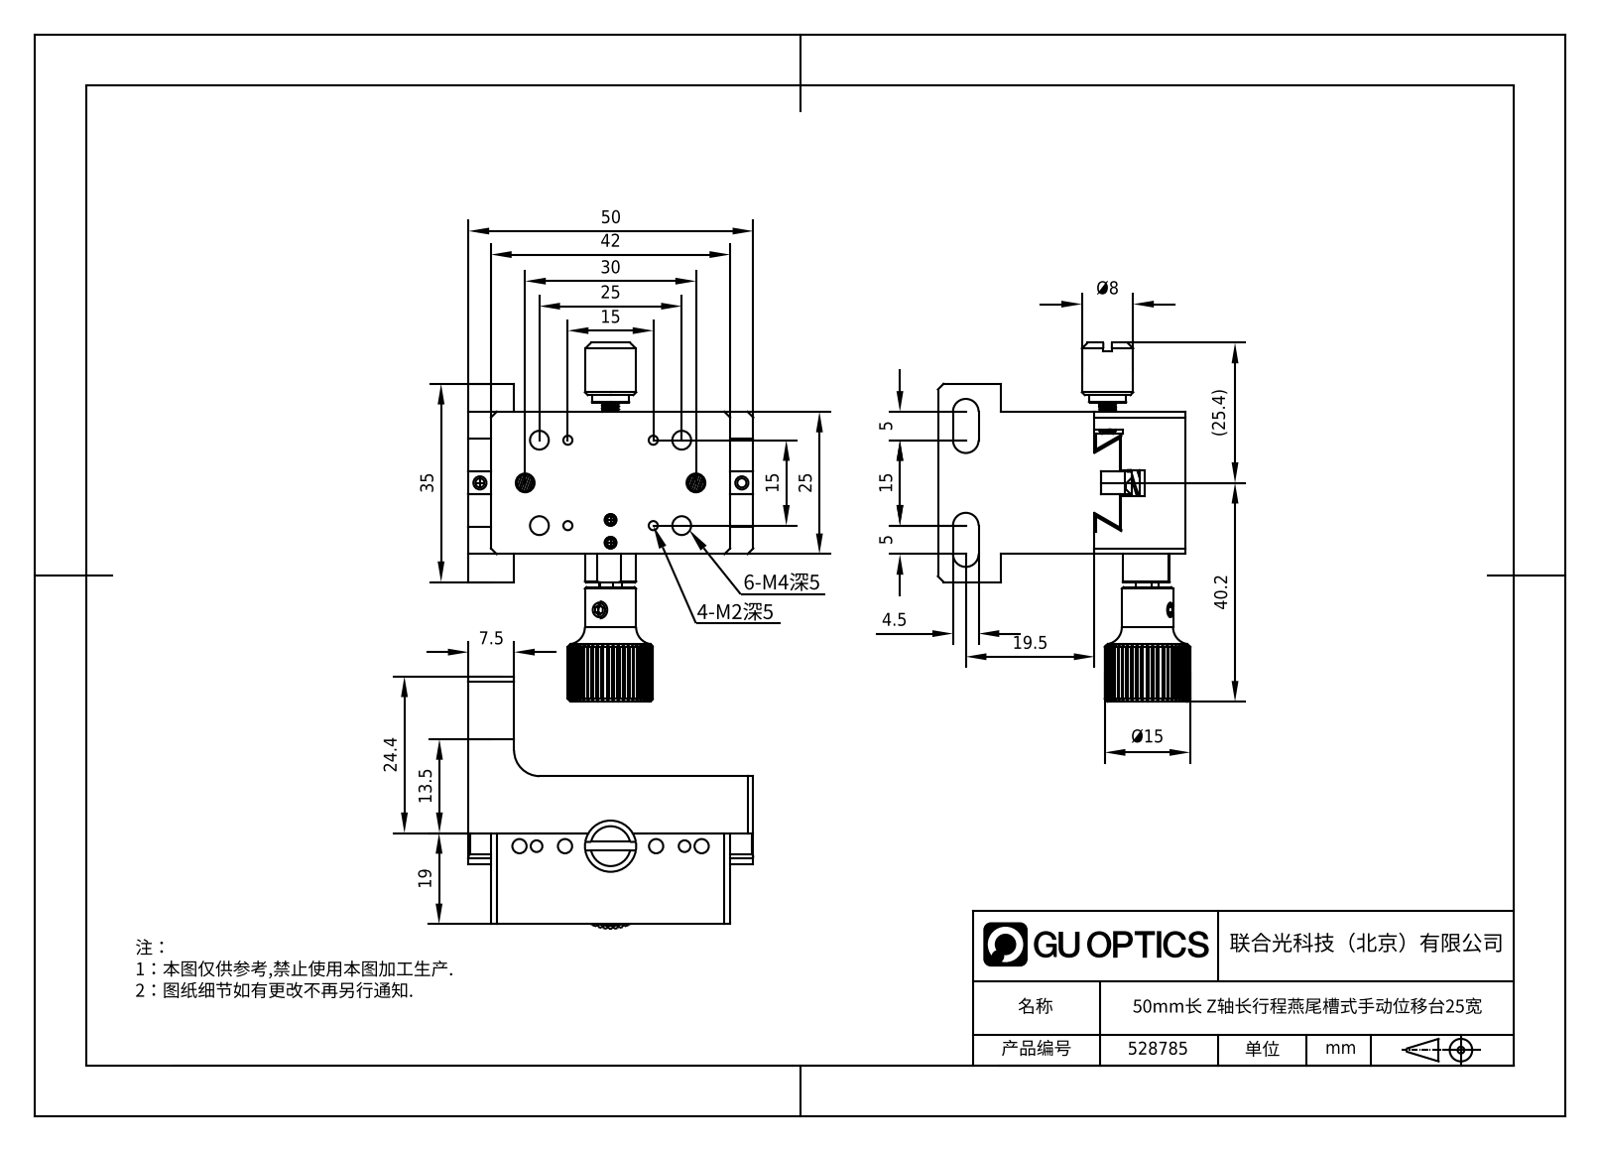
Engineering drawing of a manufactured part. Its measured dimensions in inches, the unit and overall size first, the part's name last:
Units: inches
Overall size (bounding box): 2.481 × 1.969 × 1.744
Round holes (diameter × count): ⌀0.063 ×6, ⌀0.098 ×6, ⌀0.13 ×6, ⌀0.081 ×4, ⌀0.091 ×2, ⌀0.157 ×1, ⌀0.177 ×1, ⌀0.315 ×1
Round bosses / shafts (diameter × count): ⌀0.354 ×2, ⌀0.098 ×2, ⌀0.276 ×1, ⌀0.27 ×1, ⌀0.256 ×1, ⌀0.118 ×1, ⌀0.116 ×1
Partial cylindrical surfaces — rounded edges, fillets, slot ends (radius × count): R0.008 ×8, R0.089 ×6, R0.177 ×2, R0.295 ×1
Main face-to-face distances: 0.984, 0.177, 0.63, 1.024, 0.394, 0.571, 0.453, 1.654, 0.16, 0.185
Hole centre spacings: 0.197, 0.591, 0.984, 0.311, 0.315, 0.418, 0.506, 0.622
Volume: 2.154 in³ · Surface area: 27.57 in²
Bodies: 10 solids, 980 faces (640 planar, 116 cylindrical, 224 other)
Part name (STEP PRODUCT): 528785
STEP written by: SolidWorks 2020 (CONFIG_CONTROL_DESIGN)
